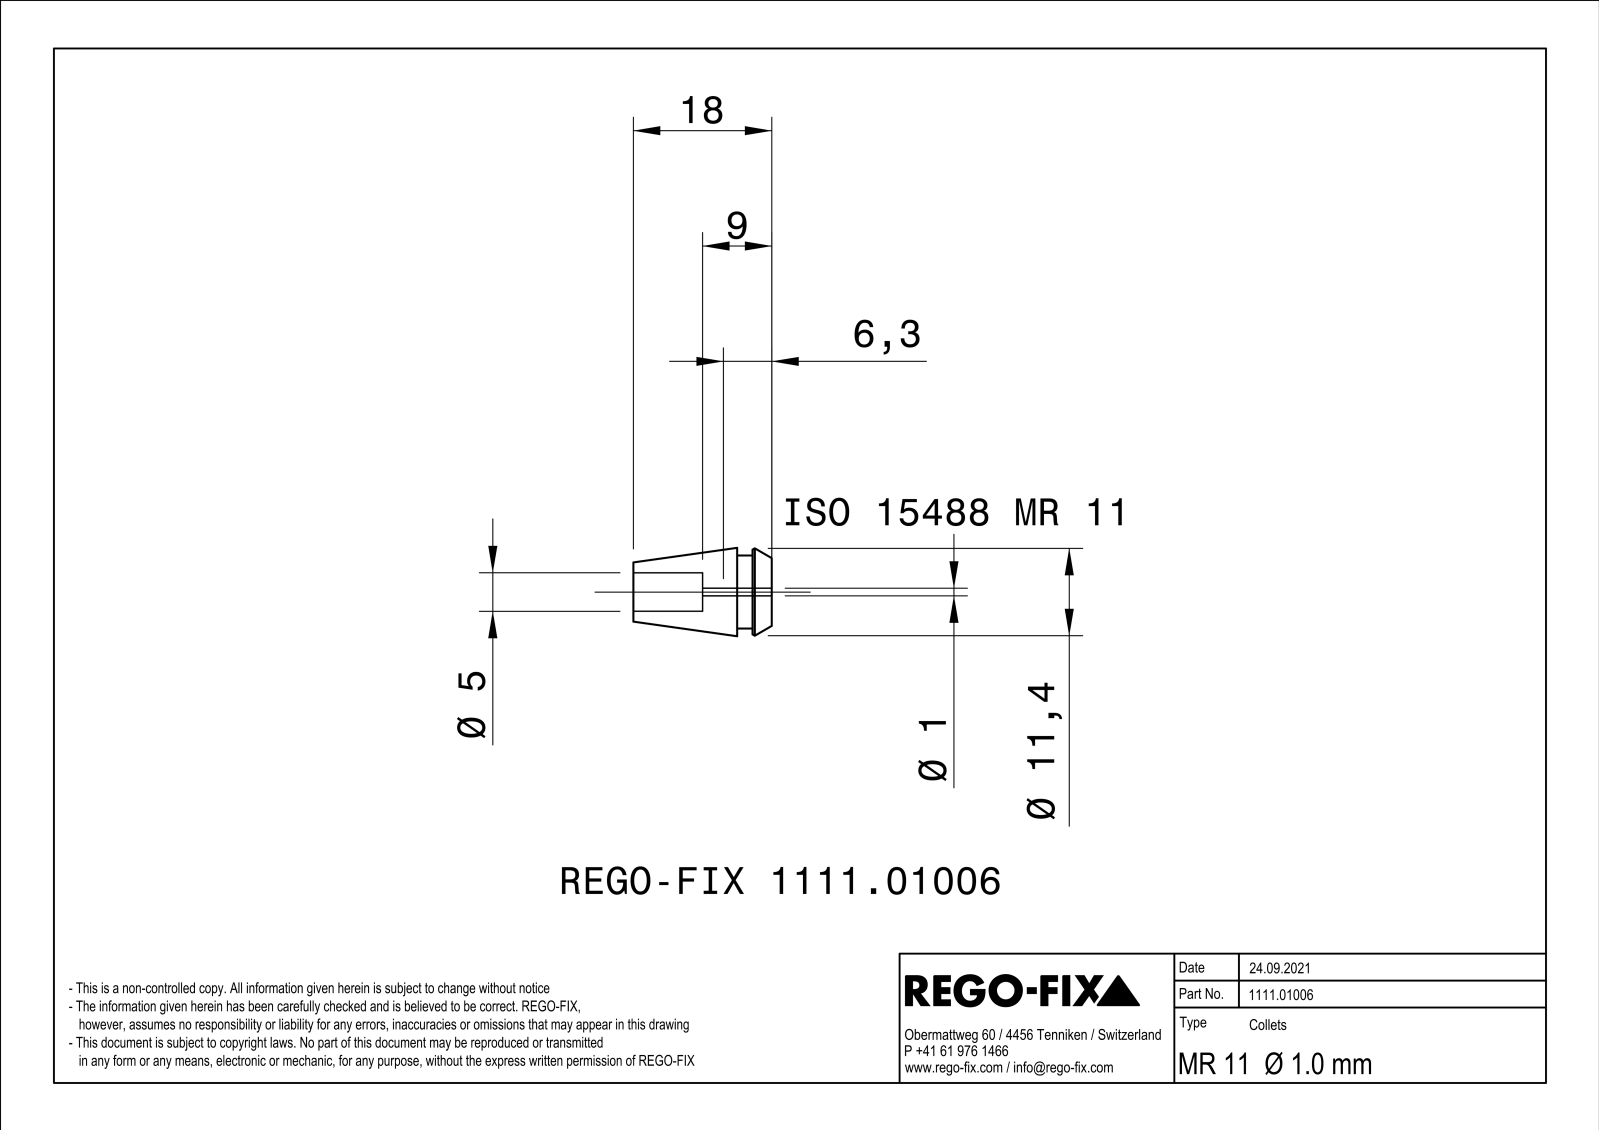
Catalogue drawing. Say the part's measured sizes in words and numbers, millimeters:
The part is named "NOCUT". Its 3-D file was written by "SIEMENS PLM Software Solid Edge ST10 (AUTOMOTIVE_DESIGN)". It is 1 solid with 289 faces: 78 planar, 65 cylindrical and 146 other. Overall it measures 18 by 11.43 by 11.43 millimeters. Its volume is 853 cubic millimeters and its surface area 2 059 square millimeters. Round holes: 1 of diameter 1. Round bosses or shafts: 1 of diameter 11.44. Partial cylindrical surfaces (rounded edges, fillets, slot ends): 24 of radius 0.23, 1 of radius 2.5, 1 of radius 4.75. The main face-to-face distances are 0.46, 0.44, 4.5, 9, 2.5, 2, 18, 15.5, 13.5, 6.5.
